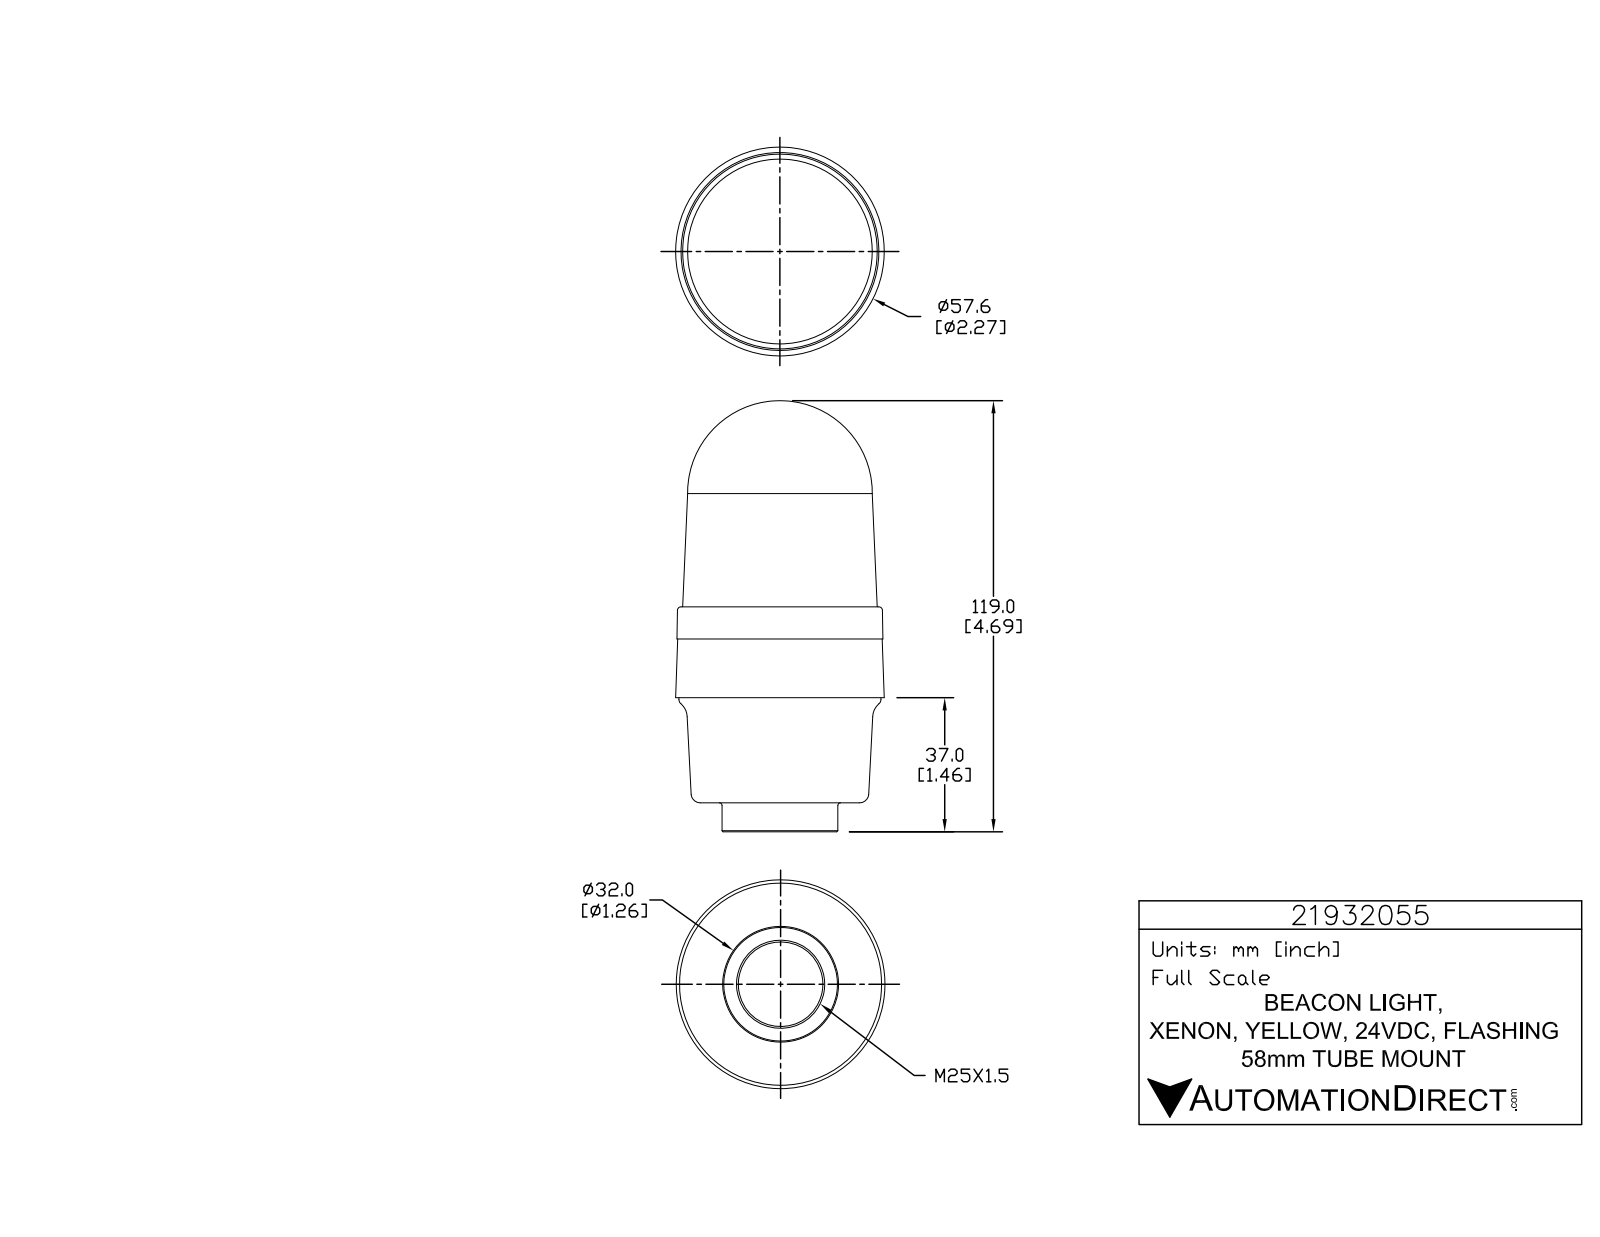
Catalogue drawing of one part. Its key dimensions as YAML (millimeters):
part_name: "21932055"
step_written_by: "SolidWorks 2015 (AUTOMOTIVE_DESIGN)"
units: millimeters
bodies: {solids: 1, faces: 791, planar: 525, cylindrical: 168, other: 98}
overall_size: [119, 57.6, 57.6]
volume: 227600
surface_area: 21970
round_holes:
  - {diameter: 1, count: 3}
  - {diameter: 23.4, count: 1}
round_bosses_or_shafts:
  - {diameter: 5.7, count: 3}
  - {diameter: 1.4, count: 3}
  - {diameter: 55.8, count: 1}
  - {diameter: 32, count: 1}
partial_cylinders:
  - {radius: 0.2, count: 6}
  - {radius: 0.2, count: 6}
  - {radius: 0.2, count: 6}
  - {radius: 3.3, count: 6}
  - {radius: 0.1, count: 3}
  - {radius: 0.1, count: 3}
  - {radius: 0.2, count: 3}
  - {radius: 0.2, count: 3}
face_to_face_distances: [8, 29, 37, 25.1, 54.1, 62.1, 8.9, 16.2, 45.2, 53.2]
